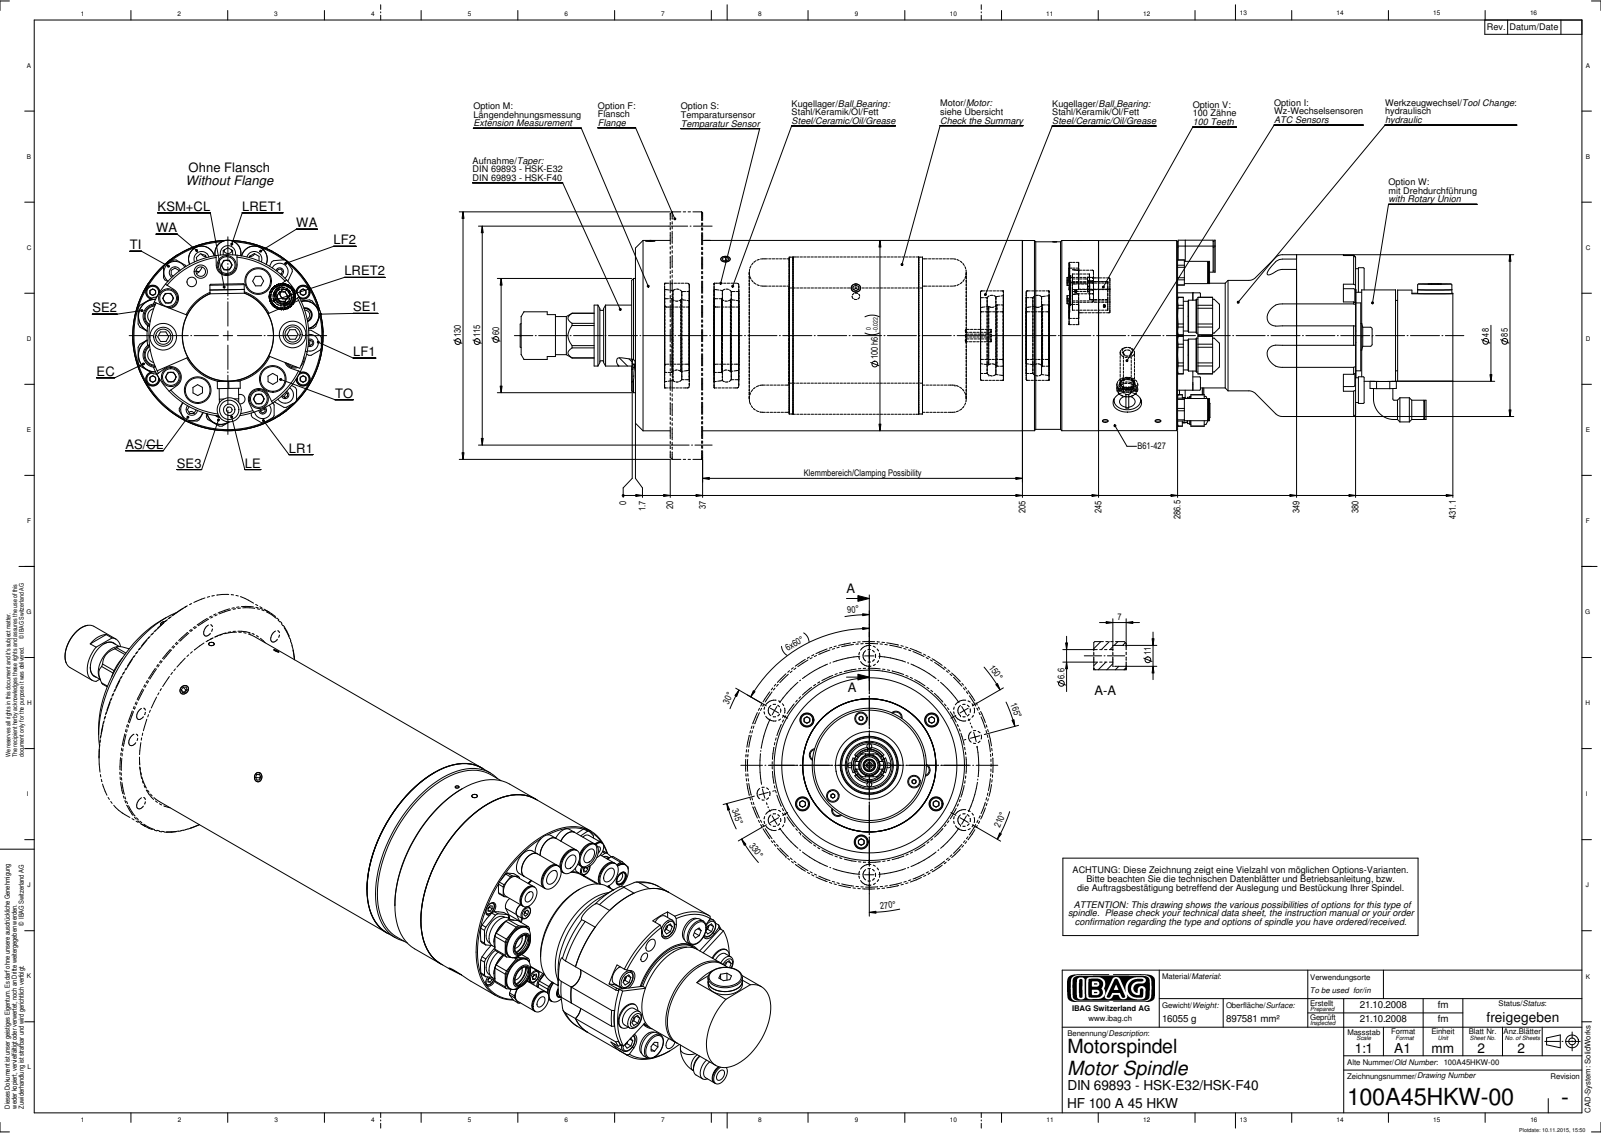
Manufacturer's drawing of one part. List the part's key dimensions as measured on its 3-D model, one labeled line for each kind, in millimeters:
Part name (STEP PRODUCT): 100A45HKW-00
STEP written by: SolidWorks 2012 (CONFIG_CONTROL_DESIGN)
Units: millimetres
Bodies: 0 solids, 1098 faces (470 planar, 409 cylindrical, 219 other)
Overall size (bounding box): 489.96 × 100.1 × 100.05
Round holes (diameter × count): ⌀7.4 ×9, ⌀8 ×6, ⌀5 ×5, ⌀4 ×4, ⌀4.5 ×3, ⌀6 ×3, ⌀15 ×3, ⌀6.7 ×2, ⌀7 ×2, ⌀10.7 ×2, ⌀16.2 ×2, ⌀10 ×1
Round bosses / shafts (diameter × count): ⌀10 ×8, ⌀14 ×7, ⌀5.7 ×6, ⌀13.7 ×4, ⌀13.7 ×4, ⌀8.8 ×4, ⌀7 ×4, ⌀7.92 ×3
Partial cylindrical surfaces — rounded edges, fillets, slot ends (radius × count): R5 ×7, R5.5 ×6, R6.6 ×6, R6 ×2, R8.25 ×2, R9.9 ×2, R11.75 ×1, R41.5 ×1
Main face-to-face distances: 243.3, 41.5, 284.8, 347.3, 104, 62.5, 18.3, 225, 378.3, 135
Hole centre spacings: 43.25, 45.6, 39.5, 40, 40.5, 72.27, 72.54, 5.1
